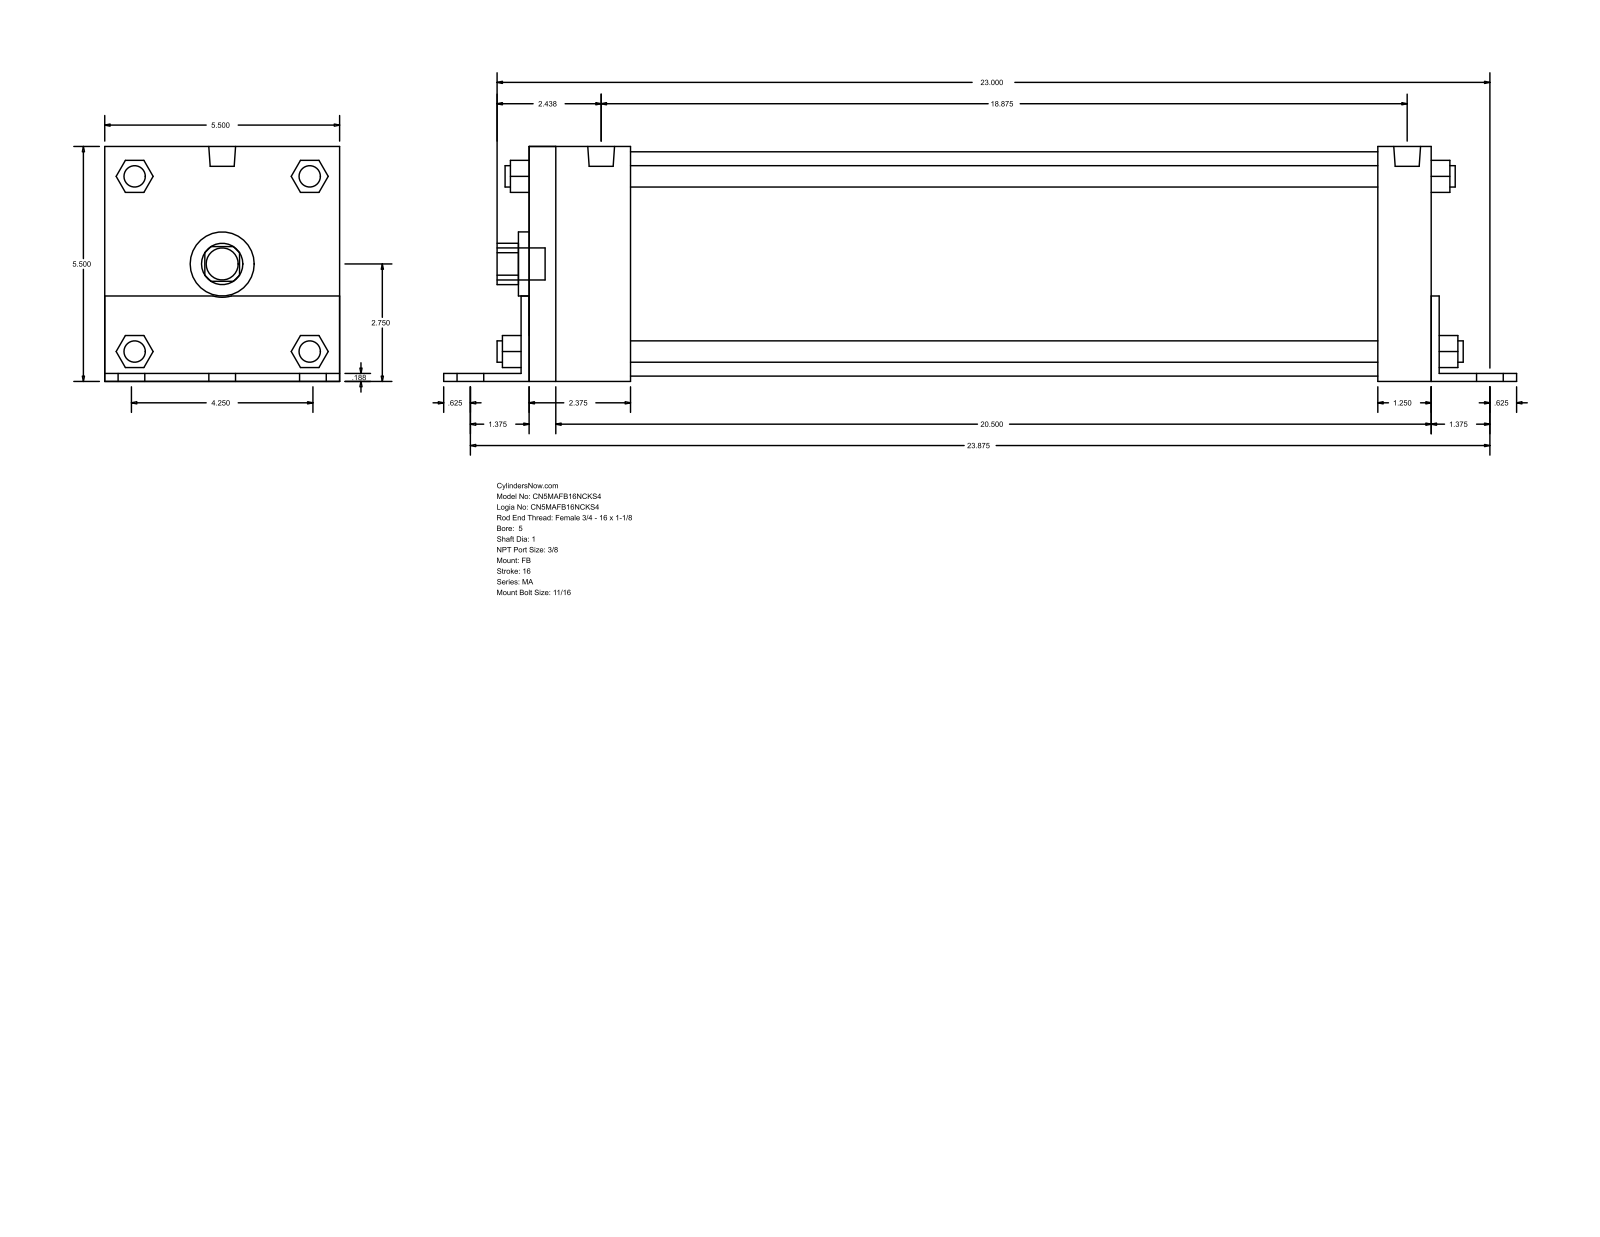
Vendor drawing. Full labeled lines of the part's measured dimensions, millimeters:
Part name (STEP PRODUCT): MA_FB__0500_1
STEP written by: GSSL Pune (CONFIG_CONTROL_DESIGN)
Units: millimetres
Bodies: 0 solids, 140 faces (105 planar, 35 cylindrical, 0 other)
Overall size (bounding box): 638.17 × 139.75 × 139.7
Round holes (diameter × count): ⌀25.4 ×1, ⌀38.1 ×1, ⌀133.35 ×1
Round bosses / shafts (diameter × count): ⌀17.46 ×6, ⌀12.7 ×4, ⌀11.11 ×4, ⌀15.93 ×2, ⌀19.05 ×1
Partial cylindrical surfaces — rounded edges, fillets, slot ends (radius × count): R12.29 ×1, R19.81 ×1
Main face-to-face distances: 139.7, 4.76, 139.75, 4.71, 134.99, 536.57, 4.77, 541.34, 546.1, 541.33
